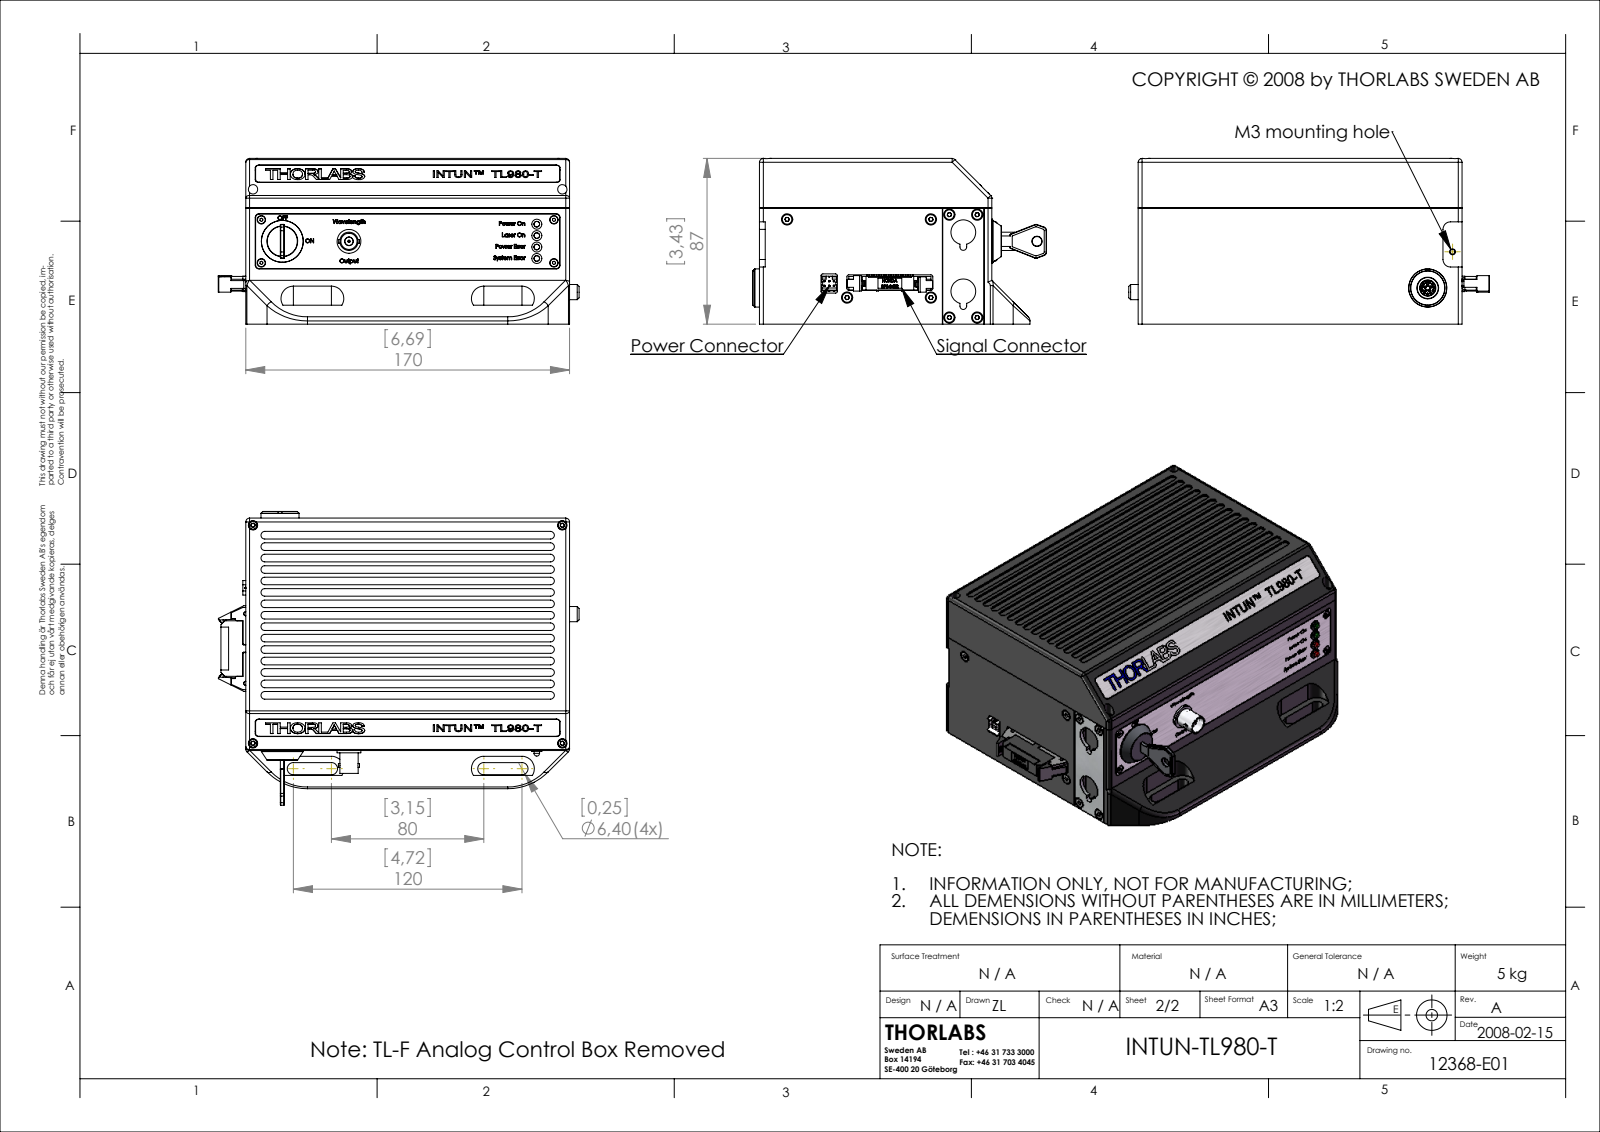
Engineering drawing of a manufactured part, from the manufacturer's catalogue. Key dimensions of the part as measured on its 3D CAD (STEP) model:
Part name (STEP PRODUCT): INTUN-TL980-T
STEP written by: SolidWorks 2007 (CONFIG_CONTROL_DESIGN)
Units: millimetres
Bodies: 0 solids, 7168 faces (4897 planar, 1137 cylindrical, 1134 other)
Overall size (bounding box): 267 × 154.2 × 110.3
Round holes (diameter × count): ⌀1 ×33, ⌀2.7 ×17, ⌀2.05 ×13, ⌀2.4 ×12, ⌀1.6 ×8, ⌀2.9 ×8, ⌀4.9 ×8, ⌀2.2 ×6, ⌀11 ×6, ⌀3 ×5, ⌀4.3 ×5, ⌀4.5 ×5
Round bosses / shafts (diameter × count): ⌀2 ×11, ⌀4 ×8, ⌀5.7 ×6, ⌀5.3 ×6, ⌀3 ×6, ⌀2.5 ×6, ⌀22 ×5, ⌀6.2 ×5
Partial cylindrical surfaces — rounded edges, fillets, slot ends (radius × count): R2 ×89, R5 ×37, R0.15 ×20, R0.99 ×20, R1.8 ×16, R0.2 ×14, R1 ×12, R6 ×12
Main face-to-face distances: 5, 1, 3, 6, 2, 6.25, 87, 86, 5.6, 84
Hole centre spacings: 3.2, 3.46, 4.84, 6.34, 1.8, 5.82, 34.06, 44
